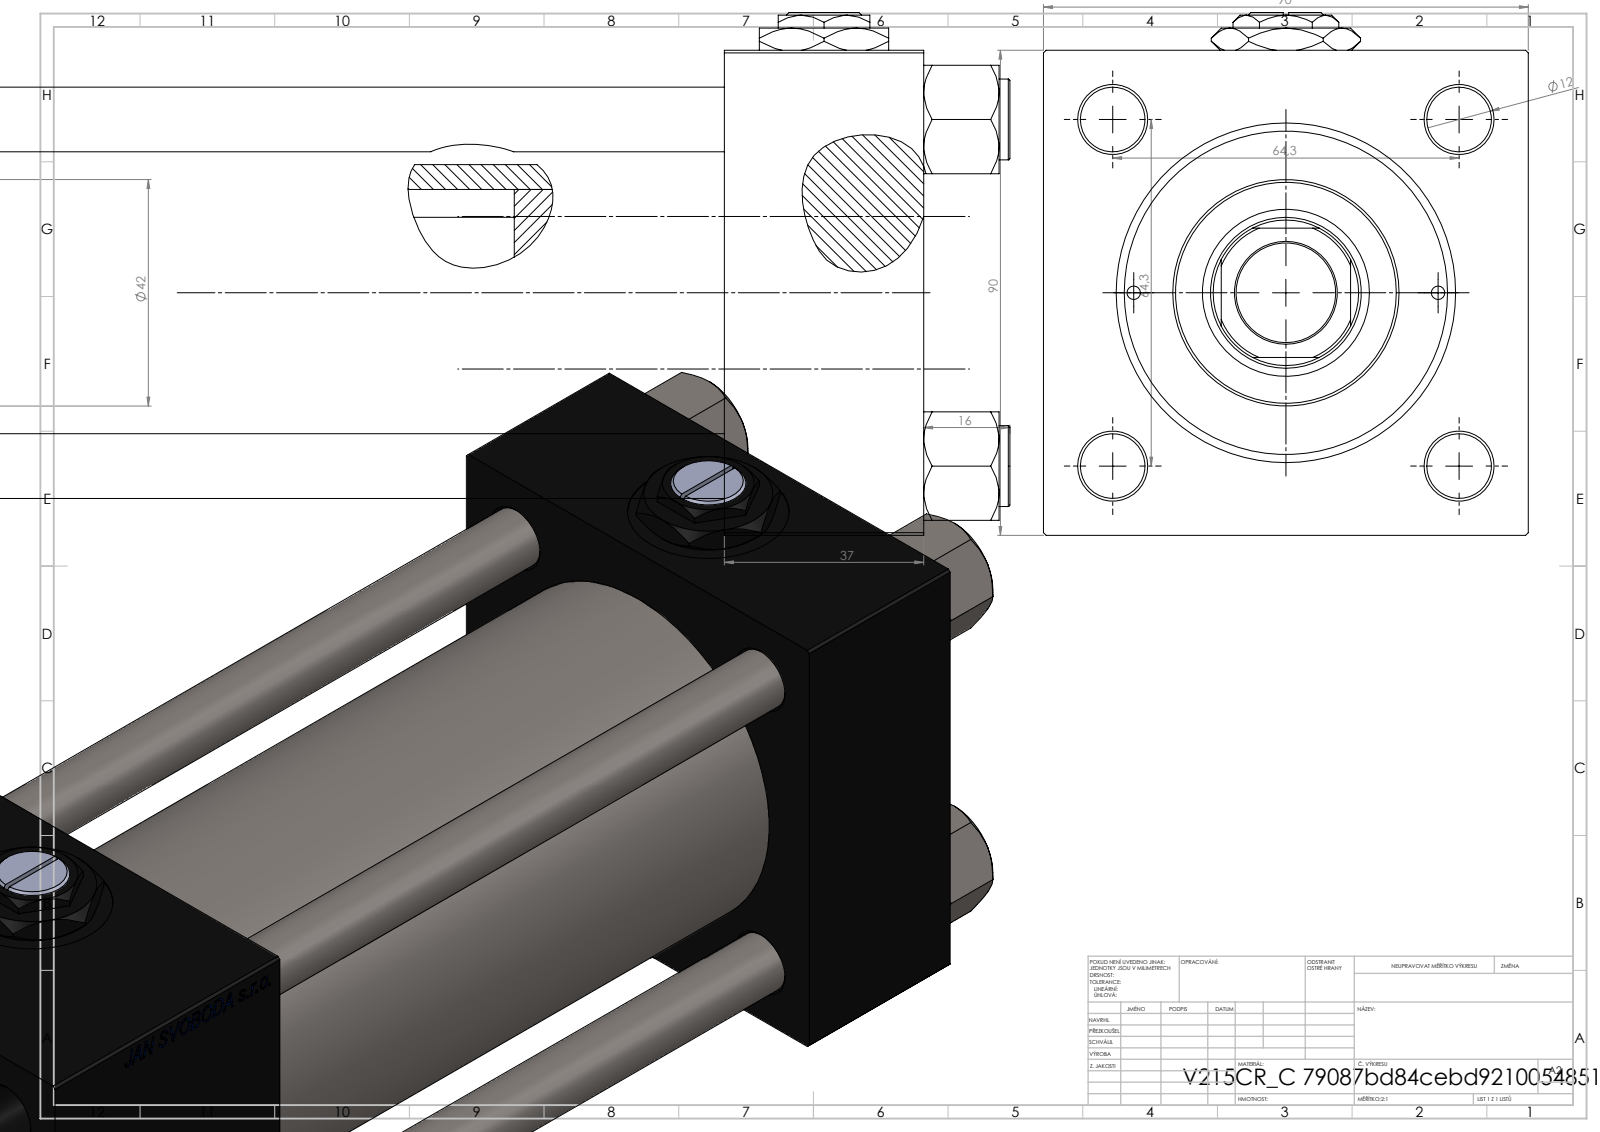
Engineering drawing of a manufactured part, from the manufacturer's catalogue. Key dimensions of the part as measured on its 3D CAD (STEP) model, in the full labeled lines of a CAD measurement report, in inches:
Part name (STEP PRODUCT): V215CR_C_Body; NUT_M5_C; Zatka_pro_OIL_PORT; V215CR_VCP_C (+2 more)
STEP written by: SolidWorks 2019 (CONFIG_CONTROL_DESIGN)
Units: inches
Bodies: 13 solids, 1256 faces (576 planar, 102 cylindrical, 578 other)
Overall size (bounding box): 11.142 × 3.819 × 3.543
Volume: 65.6 in³ · Surface area: 366.4 in²
Round holes (diameter × count): ⌀0.472 ×4, ⌀0.098 ×2, ⌀0.276 ×2, ⌀0.825 ×2, ⌀1.181 ×2, ⌀0.728 ×1, ⌀1.102 ×1, ⌀1.22 ×1, ⌀1.969 ×1, ⌀2.362 ×1, ⌀2.48 ×1
Round bosses / shafts (diameter × count): ⌀0.591 ×4, ⌀2.717 ×1, ⌀1.654 ×1
Partial cylindrical surfaces — rounded edges, fillets, slot ends (radius × count): R0.531 ×1
Main face-to-face distances: 3.543, 1.457, 7.795, 9.252, 2.323, 6.929, 5.472, 8.122, 6.665, 1.193
Hole centre spacings: 1.275, 1.79, 2.531, 2.694, 1.112, 3.58, 2.224, 6.988
